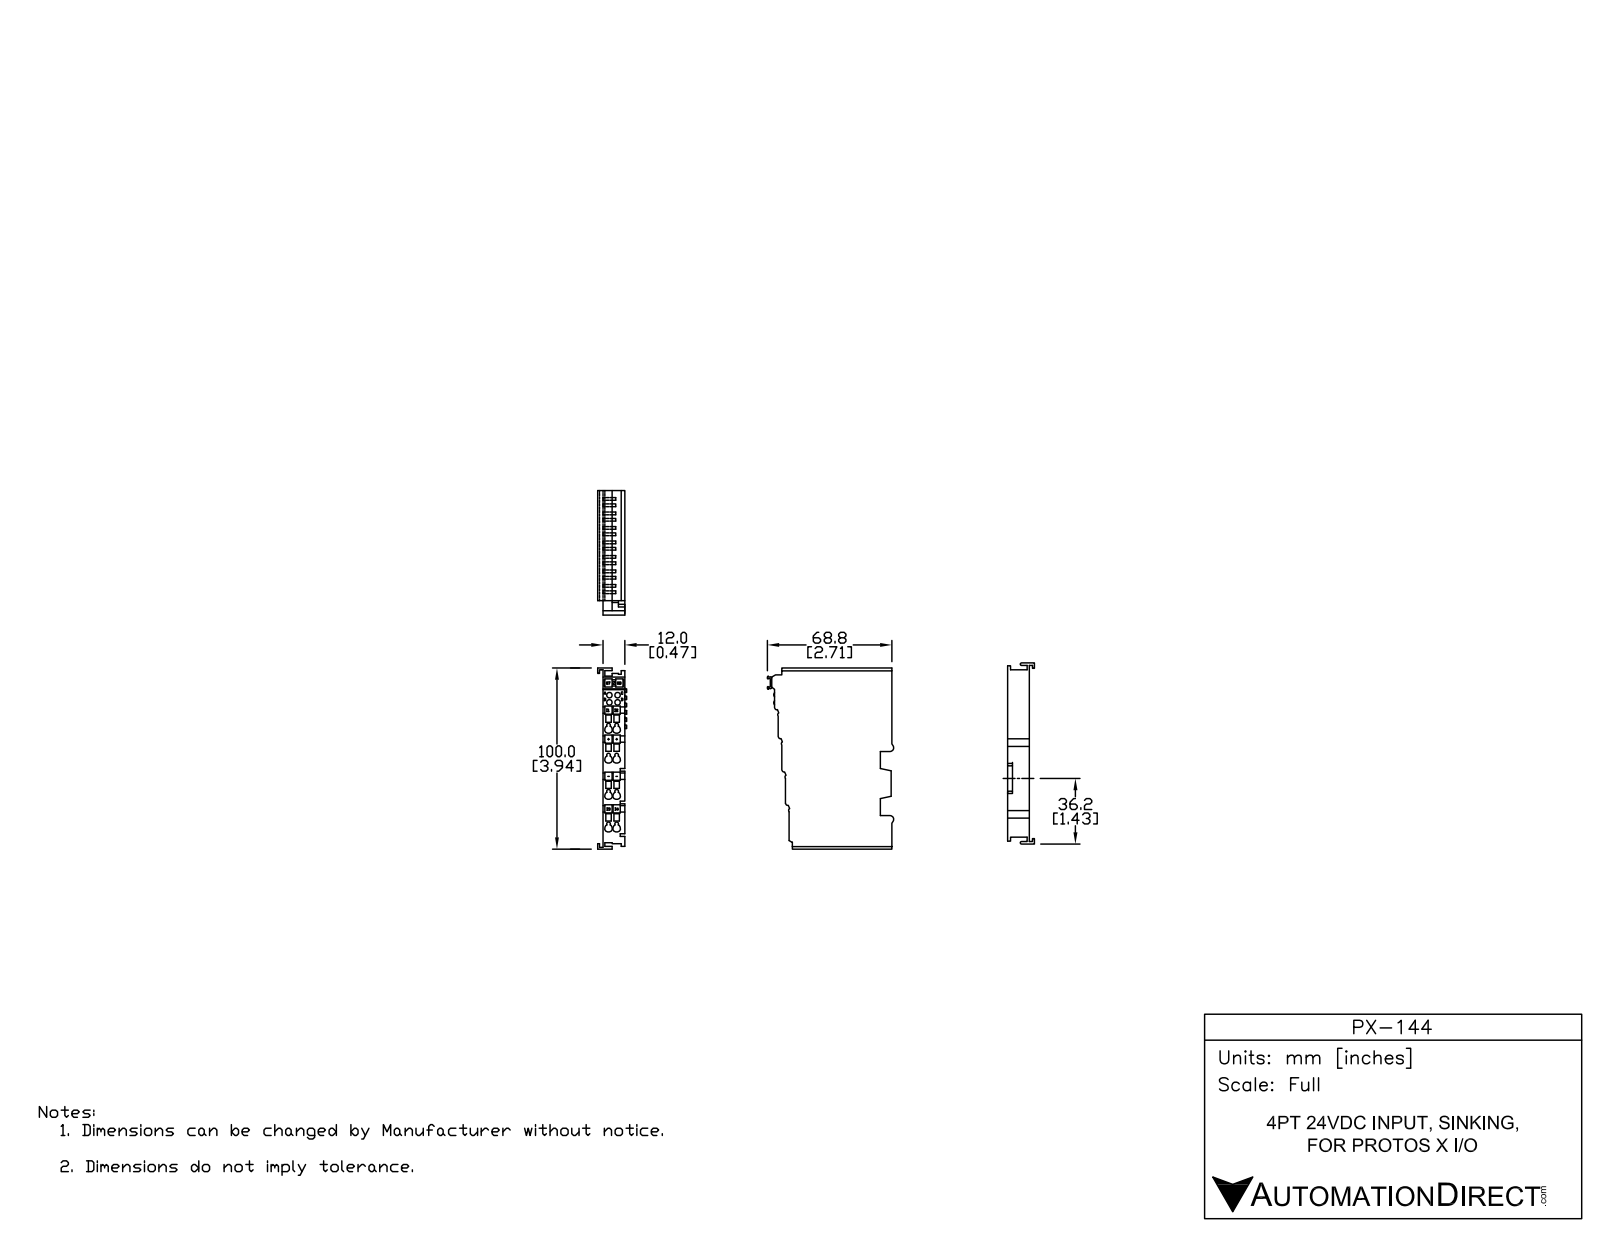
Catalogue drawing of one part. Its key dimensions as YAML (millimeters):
part_name: "PX-144"
step_written_by: "SolidWorks 2014 (AUTOMOTIVE_DESIGN)"
units: millimeters
bodies: {solids: 28, faces: 1367, planar: 963, cylindrical: 344, other: 60}
overall_size: [100.25, 71.26, 15.15]
volume: 58403
surface_area: 33884
round_holes:
  - {diameter: 4, count: 8}
  - {diameter: 3.5, count: 4}
partial_cylinders:
  - {radius: 0.3, count: 46}
  - {radius: 0.25, count: 35}
  - {radius: 0.38, count: 12}
  - {radius: 0.12, count: 10}
  - {radius: 1, count: 9}
  - {radius: 0.4, count: 8}
  - {radius: 0.17, count: 4}
  - {radius: 1.03, count: 4}
face_to_face_distances: [12, 1, 2, 10, 1.85, 11, 8.7, 4, 3.15, 1.22]
hole_center_spacings: [4.5, 5, 18.4, 19.07, 6.36, 16, 16.76, 20.41]
